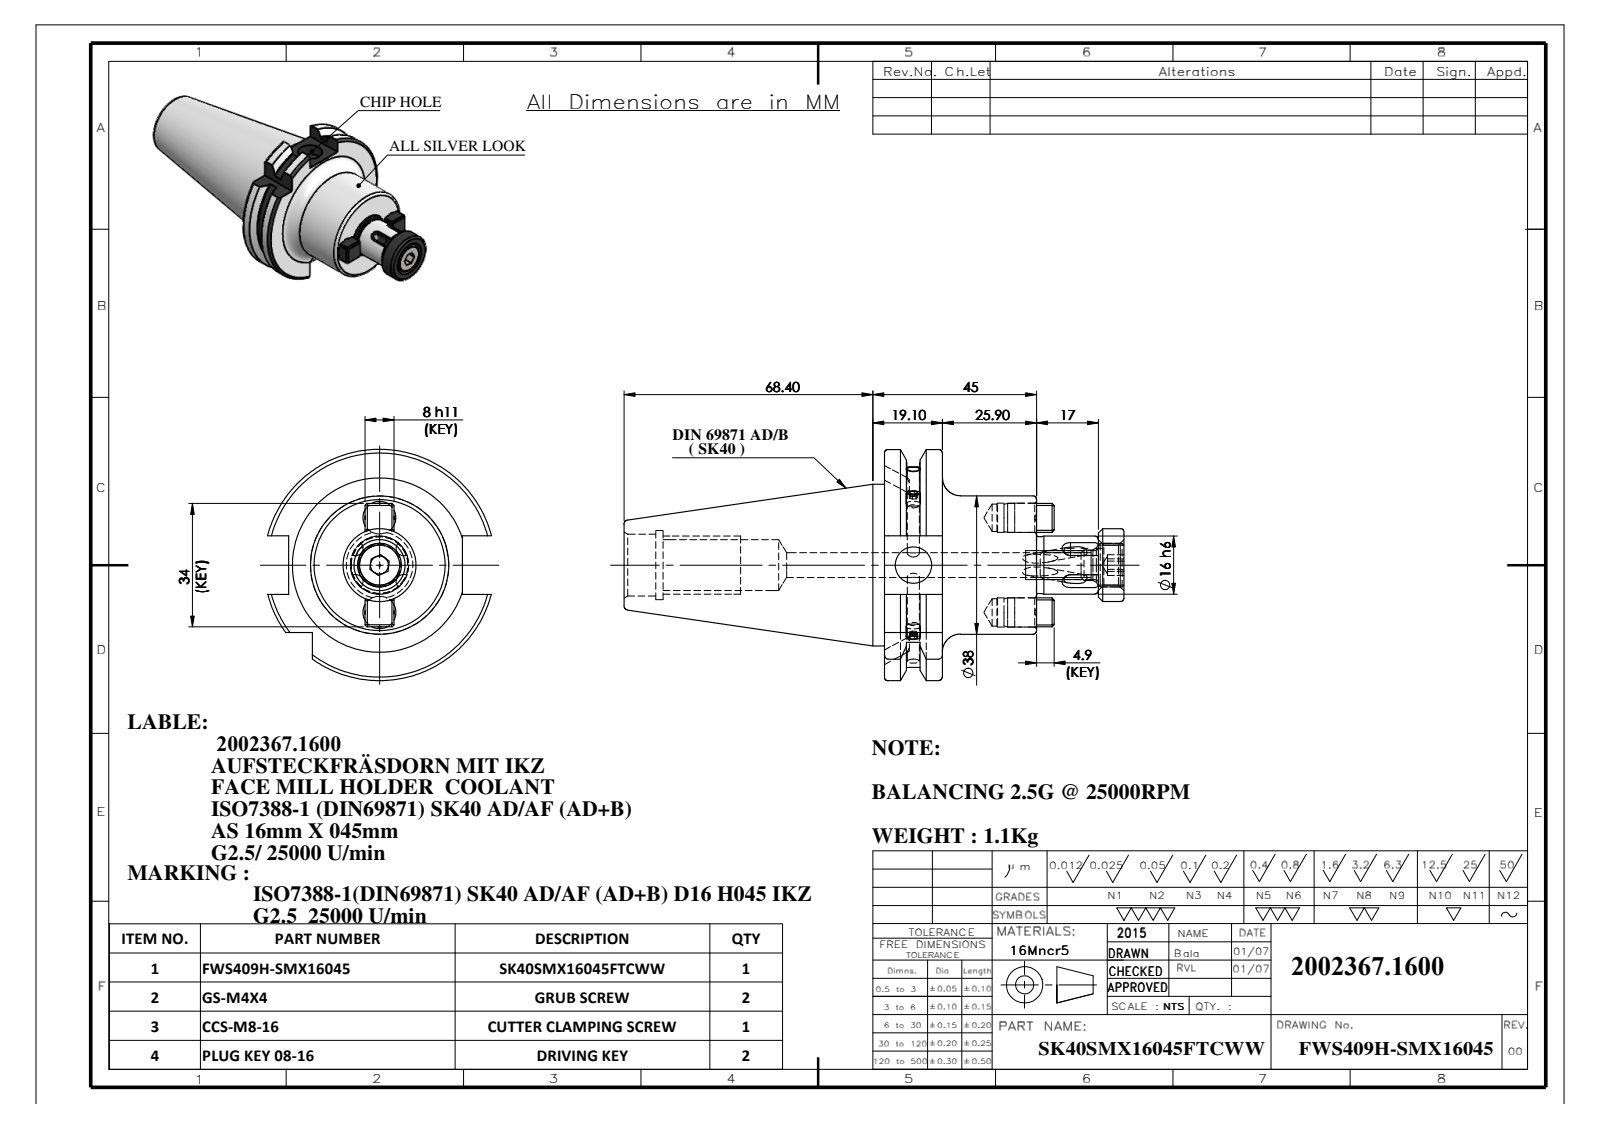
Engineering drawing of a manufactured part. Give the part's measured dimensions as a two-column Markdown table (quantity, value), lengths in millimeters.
| quantity | value |
| --- | --- |
| part name | SK40SMS16045FTCWW; CCS-M8-16-1-SHORT LENGHT; CCS-M8-16-2; CCS-M8-16-SHORT LENGHT (+3 more) |
| STEP written by | SolidWorks 2018 (CONFIG_CONTROL_DESIGN) |
| units | millimeters |
| bodies | 7 solids, 321 faces (110 planar, 88 cylindrical, 123 other) |
| overall size | 137.4 × 63.55 × 61.48 |
| volume | 137 838 mm³ |
| surface area | 28 995 mm² |
| round holes (diameter × count) | 3 × 4, 7.5 × 2, 8 × 2, 3.3 × 1, 6.8 × 1, 8.4 × 1, 10 × 1, 11 × 1, 14 × 1, 17 × 1, 19 × 1 |
| round bosses / shafts (diameter × count) | 8.02 × 2, 7.98 × 2, 4 × 2, 44.45 × 1, 38 × 1, 20 × 1, 16 × 1, 15.6 × 1 |
| partial cylindrical surfaces (radius × count) | 2 × 4, 5.25 × 2, 28.12 × 1, 31.77 × 1 |
| main face-to-face distances | 15.9, 41.8, 25.9, 65.8, 49.9, 24, 16.1, 47.8, 7, 58.8 |
| hole center spacings | 13, 26 |
